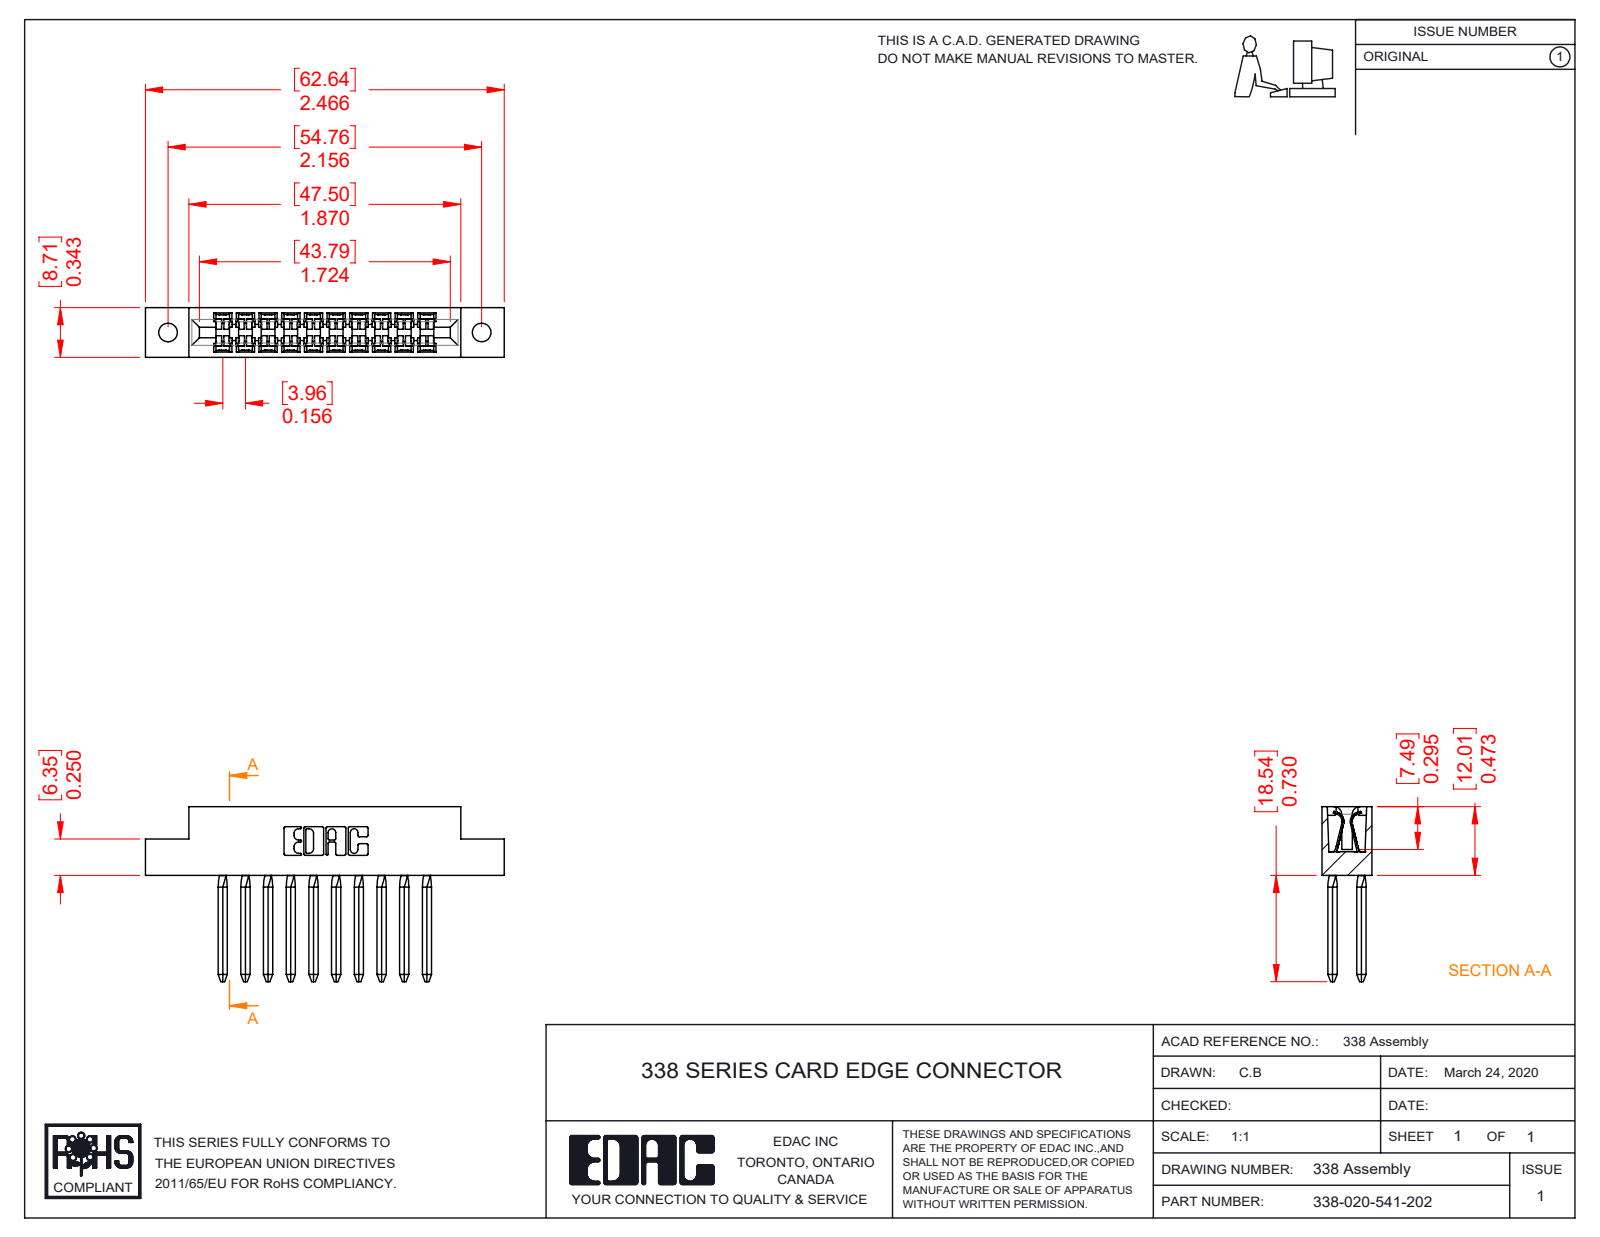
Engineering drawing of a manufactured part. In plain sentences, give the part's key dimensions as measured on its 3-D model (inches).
The part is named "338-020-541-202; 338-210-001_338-210-010-002; 338-290-001_541". Its 3-D file was written by "SolidWorks 2016 (CONFIG_CONTROL_DESIGN)". It is 21 solids with 1434 faces: 990 planar, 364 cylindrical and 80 other. Overall it measures 2.466 by 1.203 by 0.343 inches. Its volume is 0.283 cubic inches and its surface area 11.8 square inches. Round holes: 2 of diameter 0.128. Partial cylindrical surfaces (rounded edges, fillets, slot ends): 62 of radius 0.025, 22 of radius 0.01, 20 of radius 0.008, 16 of radius 0.055, 16 of radius 0.067, 16 of radius 0.1, 6 of radius 0.007, 6 of radius 0.031. The main face-to-face distances are 0.343, 0.156, 0.11, 0.25, 0.624, 0.468, 0.221, 0.296, 0.406, 0.312. The hole center spacings are 2.156.
